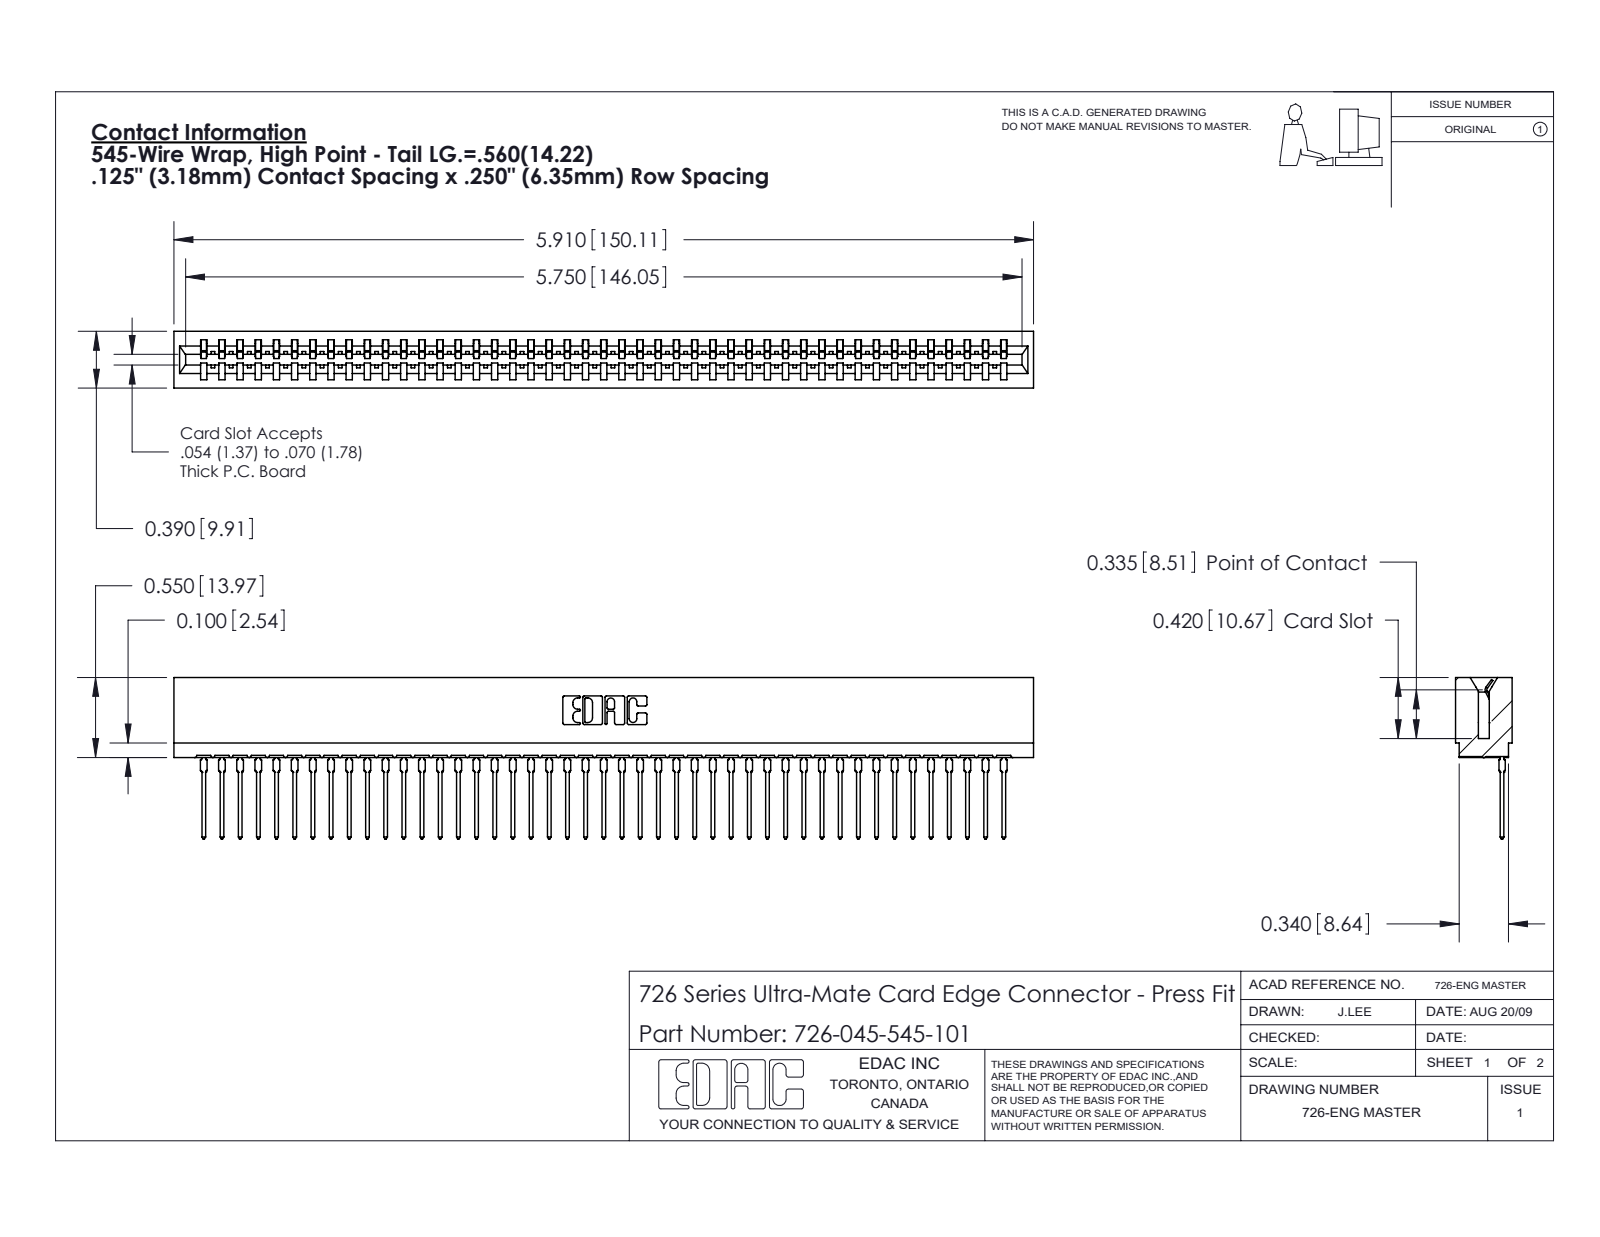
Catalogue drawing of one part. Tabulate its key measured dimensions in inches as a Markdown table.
| quantity | value |
| --- | --- |
| part name | 746-292-001_545; 726-045-545-101; 726 Part_.515 Slot Depth - 01 |
| STEP written by | SolidWorks 2020 (CONFIG_CONTROL_DESIGN) |
| units | inches |
| bodies | 46 solids, 4957 faces (2890 planar, 897 cylindrical, 1170 other) |
| overall size | 5.91 × 1.109 × 0.39 |
| volume | 0.824 in³ |
| surface area | 33 in² |
| partial cylindrical surfaces (radius × count) | 0.021 × 90, 0.015 × 46, 0.01 × 22, 0.007 × 6, 0.031 × 6, 0.005 × 4, 0.011 × 4, 0.026 × 3 |
| main face-to-face distances | 0.057, 0.333, 0.39, 0.025, 0.307, 0.25, 0.083, 0.275, 0.365, 0.032 |
